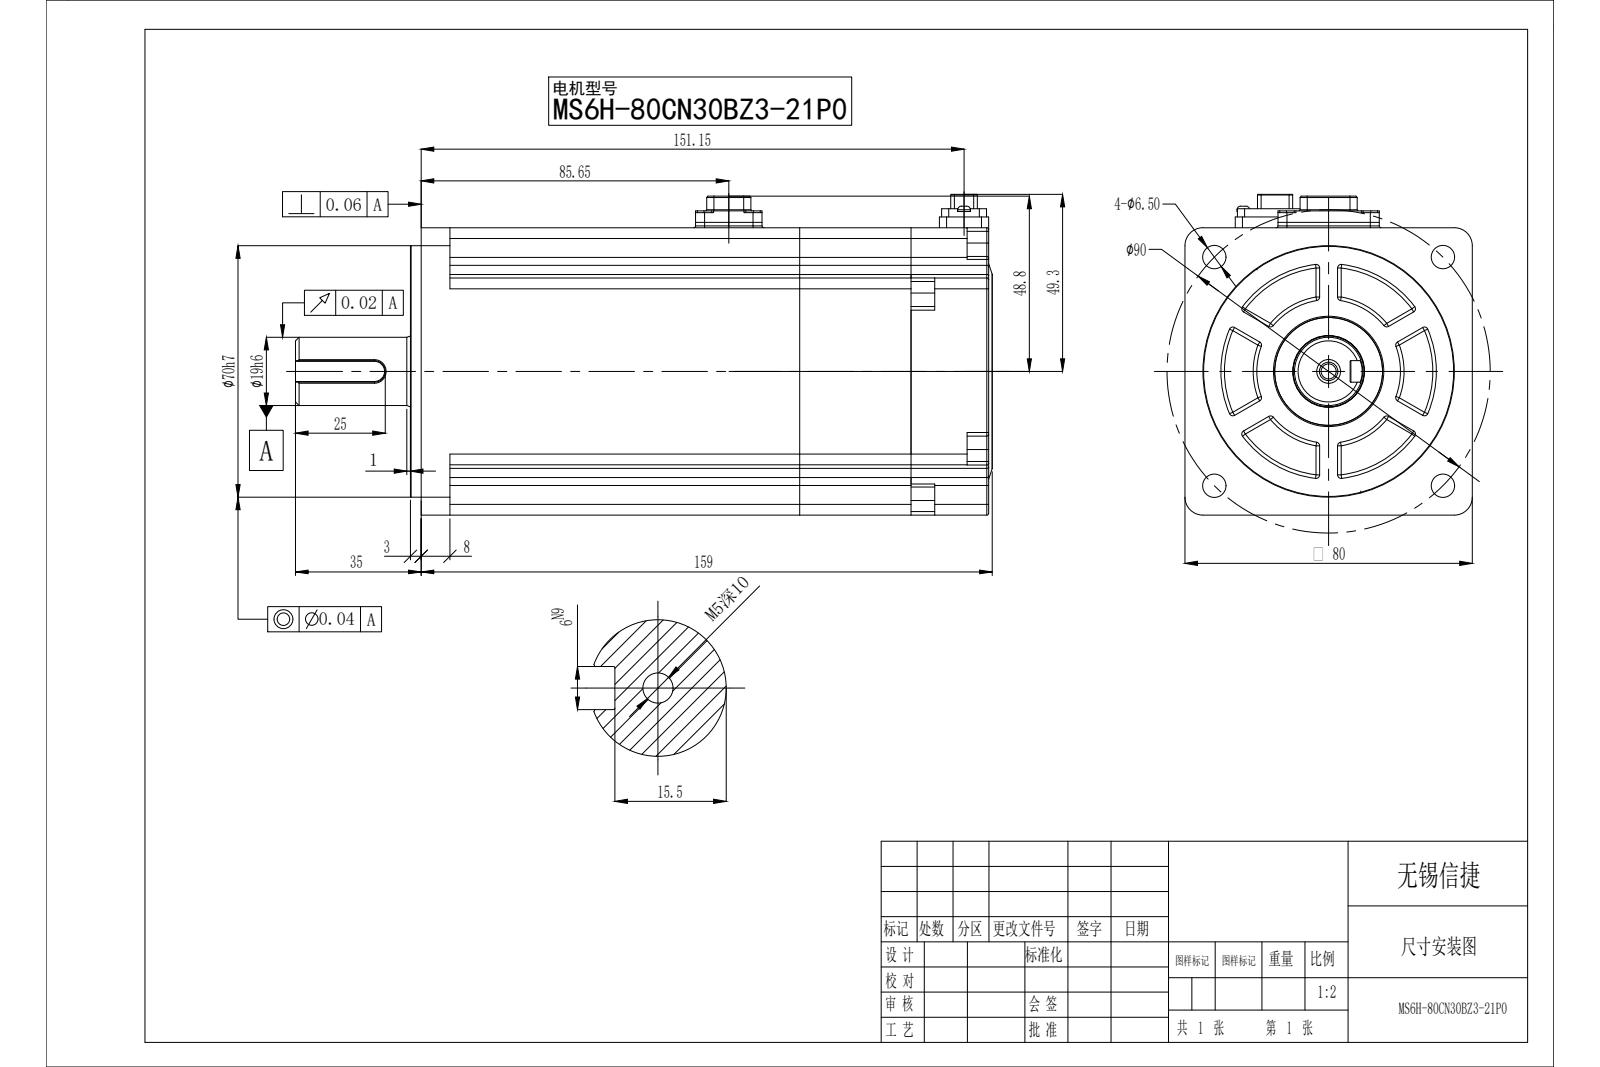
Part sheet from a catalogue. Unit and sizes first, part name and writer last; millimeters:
Units: millimetres
Overall size (bounding box): 194 × 89.3 × 80
Round holes (diameter × count): ⌀2.1 ×4, ⌀6.5 ×4, ⌀1.6 ×2, ⌀4.2 ×1, ⌀20 ×1
Round bosses / shafts (diameter × count): ⌀7 ×8, ⌀5.6 ×4, ⌀4 ×4, ⌀3.5 ×2, ⌀70 ×1, ⌀30 ×1, ⌀19.8 ×1, ⌀19 ×1
Partial cylindrical surfaces — rounded edges, fillets, slot ends (radius × count): R1 ×50, R0.5 ×32, R0.2 ×20, R3 ×17, R2 ×12, R0.3 ×11, R3.75 ×8, R0.6 ×4
Main face-to-face distances: 80, 14, 66, 52, 158, 159, 1, 3, 161, 162
Hole centre spacings: 45, 63.64, 8, 16.6, 18.43, 90, 23.5, 61.72
Bodies: 0 solids, 822 faces (369 planar, 304 cylindrical, 149 other)
STEP written by: SolidWorks 2016 (CONFIG_CONTROL_DESIGN)
